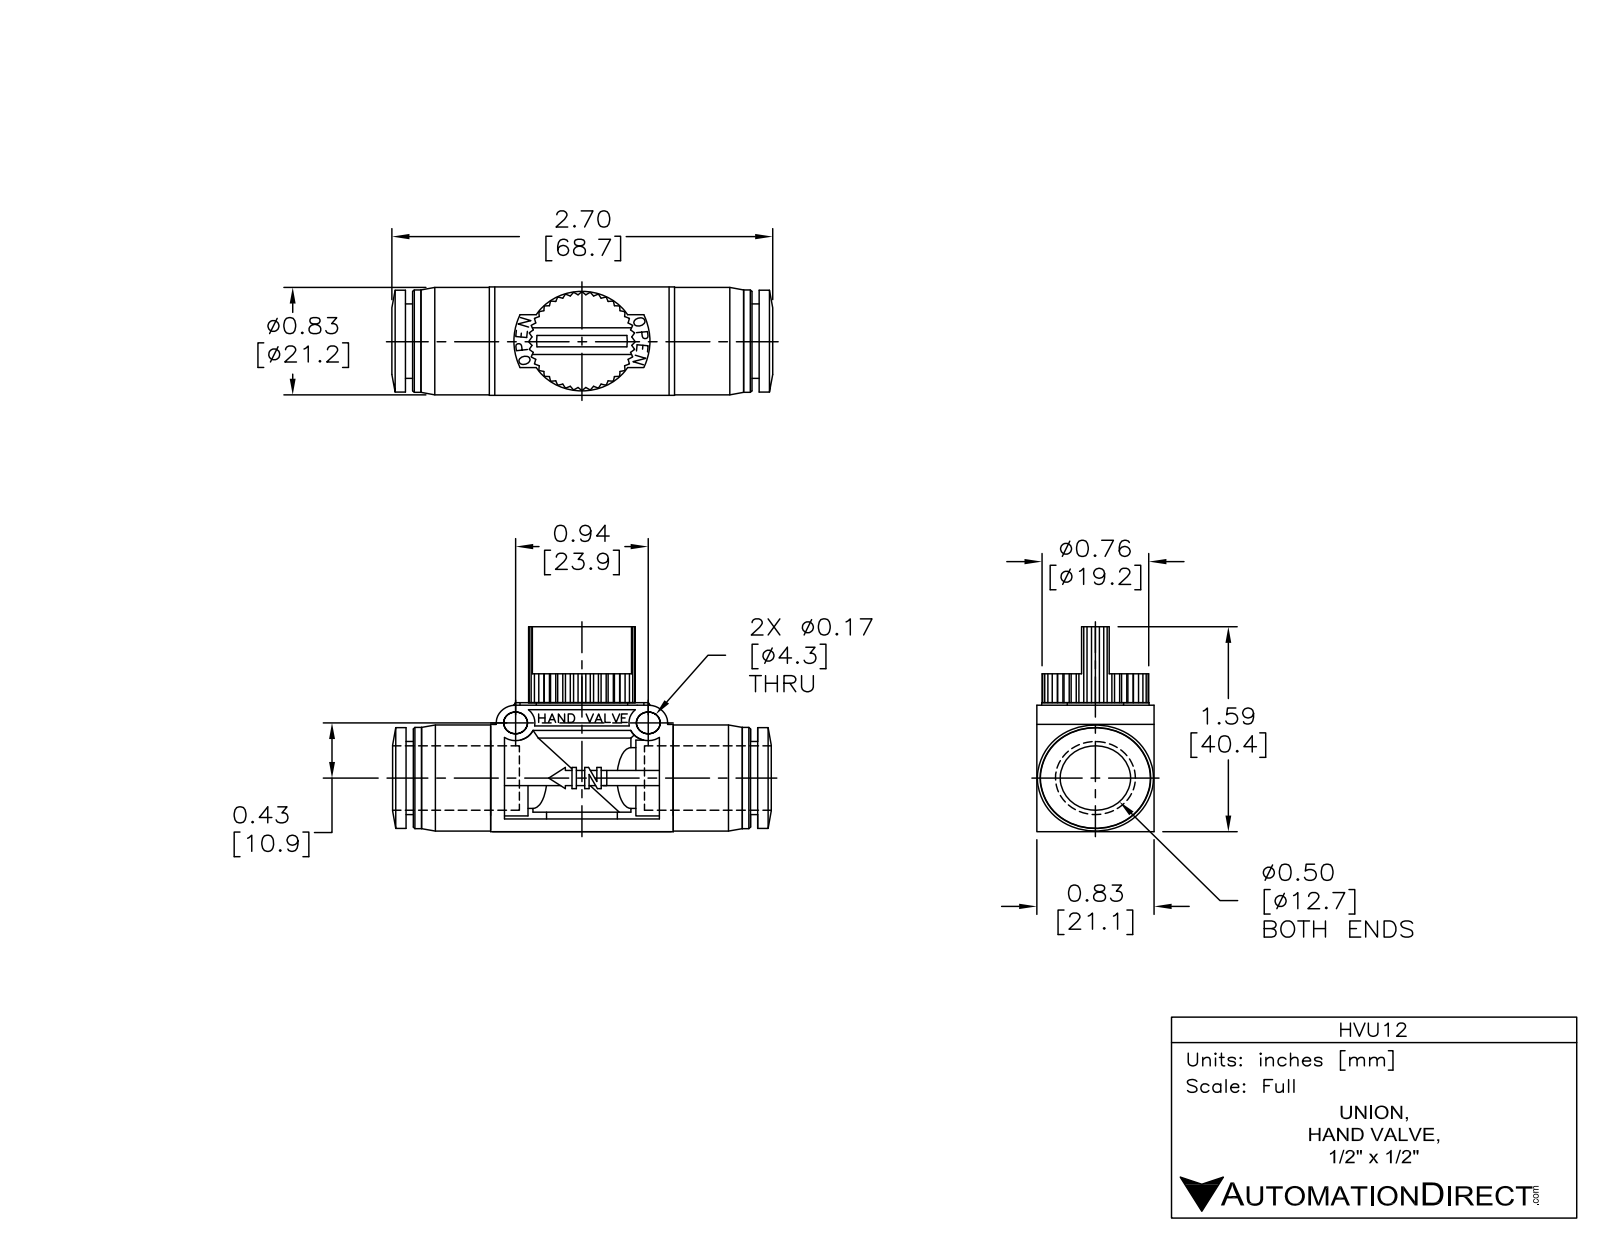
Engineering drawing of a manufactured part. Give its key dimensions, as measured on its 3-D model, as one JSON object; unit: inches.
{"part_name": "HVU12", "step_written_by": "SolidWorks 2015 (AUTOMOTIVE_DESIGN)", "units": "inches", "bodies": {"solids": 1, "faces": 303, "planar": 212, "cylindrical": 60, "other": 31}, "overall_size": [2.697, 1.594, 0.835], "volume_in3": 1.256, "surface_area_in2": 18.45, "round_holes": [[0.169, 2], [0.51, 1]], "round_bosses_or_shafts": [[0.807, 1], [0.787, 1], [0.783, 1], [0.701, 1], [0.697, 1], [0.591, 1], [0.569, 1]], "partial_cylinders_radius": [[0.138, 2], [0.24, 1], [0.252, 1], [0.407, 1]], "face_to_face_distances": [0.098, 0.319, 0.516, 0.835, 0.059, 0.378, 0.457, 0.051, 0.138, 1.752], "hole_center_spacings": [0.945]}
